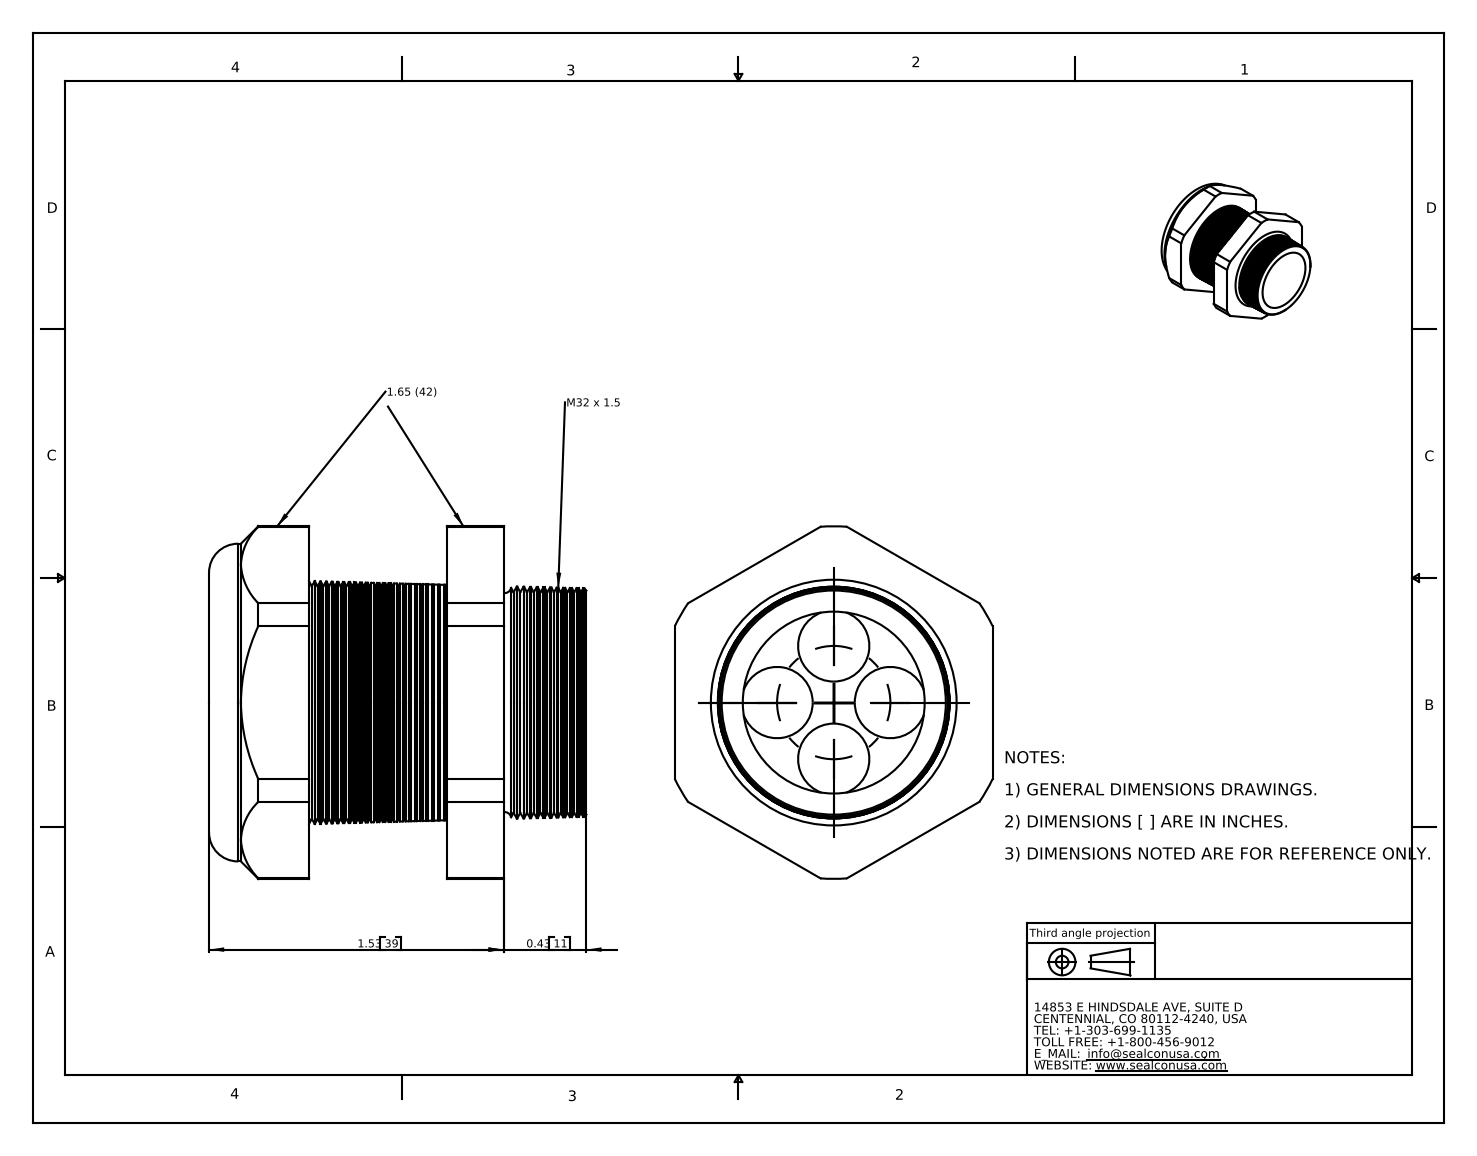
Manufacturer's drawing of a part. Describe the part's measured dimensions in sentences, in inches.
The part is named "CD32M3-GY". Its 3-D file was written by "SolidWorks 2007 (CONFIG_CONTROL_DESIGN)". It is 2 solids with 279 faces: 21 planar, 28 cylindrical and 230 other. Overall it measures 1.96 by 1.831 by 1.65 inches. Its volume is 1.87 cubic inches and its surface area 27.37 square inches. Round holes: 4 of diameter 0.37, 1 of diameter 0.96, 1 of diameter 0.98. Round bosses or shafts: 1 of diameter 1.65. Partial cylindrical surfaces (rounded edges, fillets, slot ends): 1 of radius 0.916. The main face-to-face distances are 0.715, 1.011, 0.295, 1.65, 0.52, 1.235, 1.53, 1.65, 1.96, 1.441. The hole center spacings are 0.294, 0.416, 0.588.
